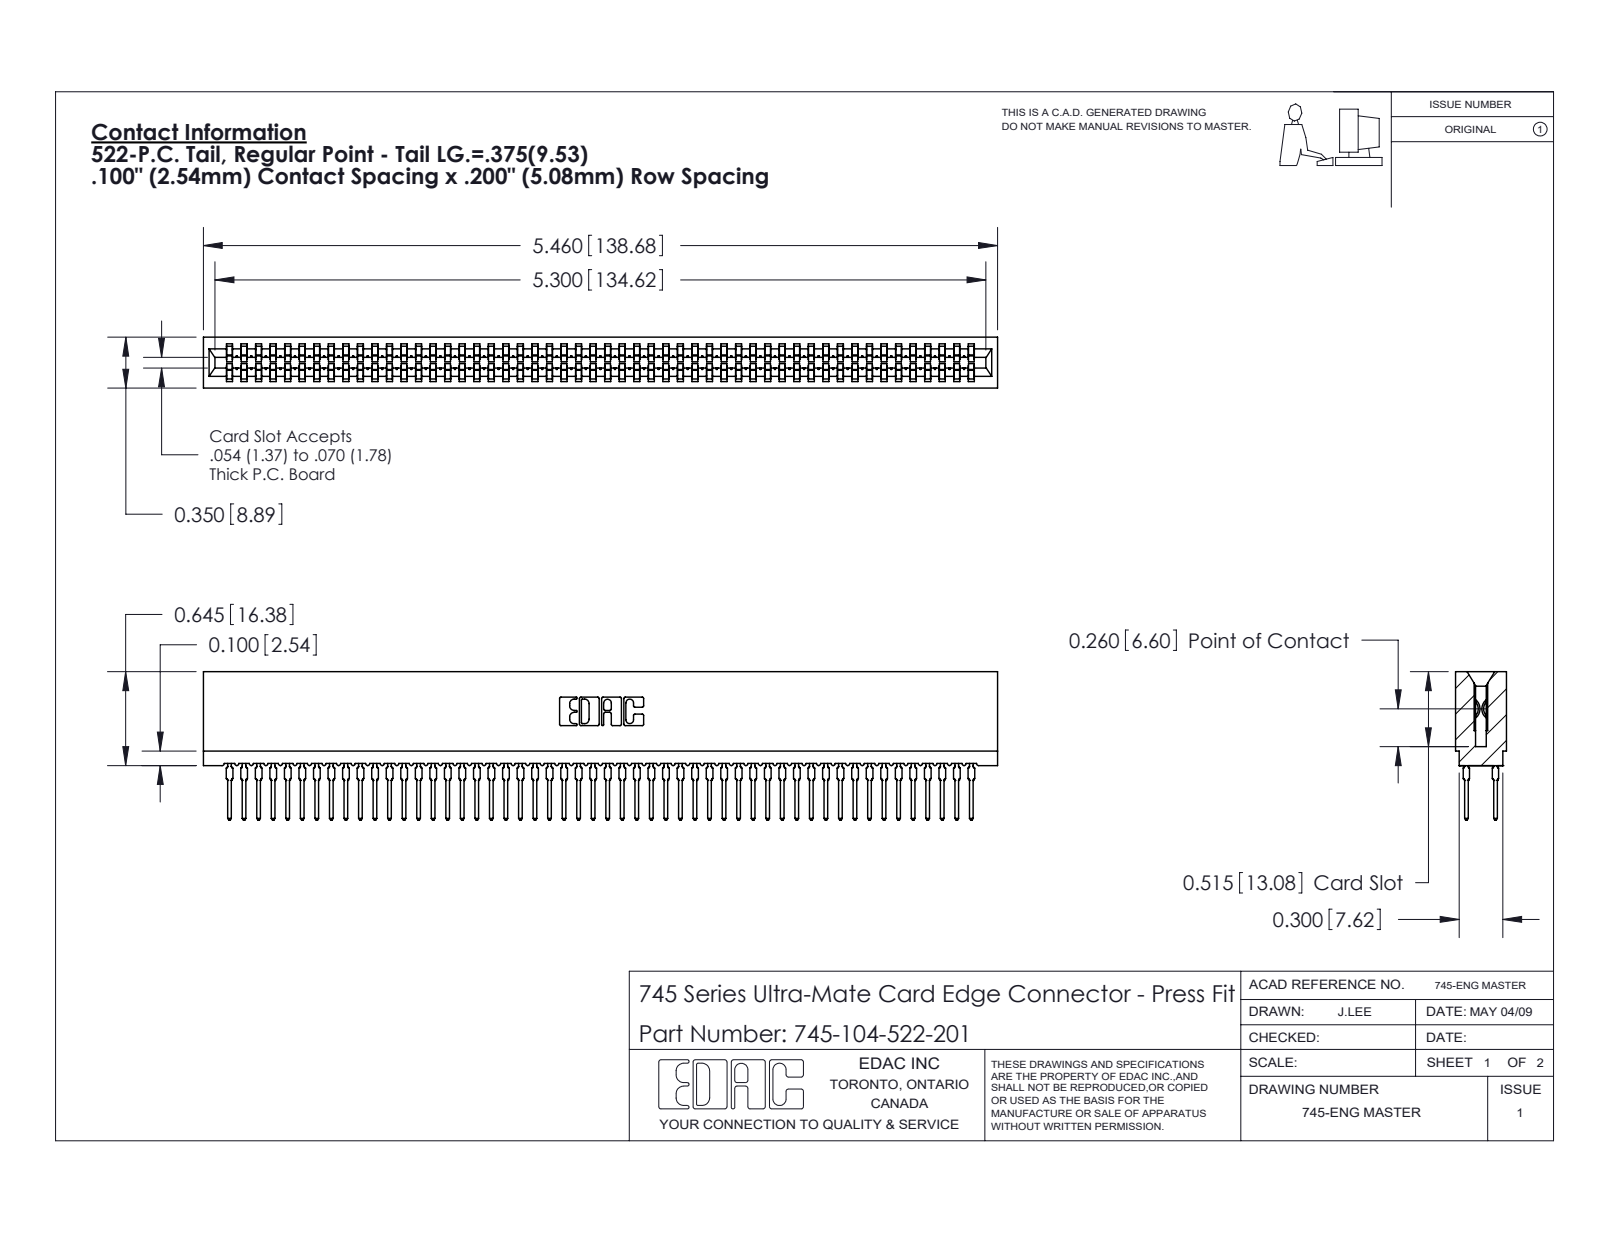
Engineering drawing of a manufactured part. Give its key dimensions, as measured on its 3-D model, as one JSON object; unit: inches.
{"part_name": "745-292-001_522; 745-104-522-201; 745 Part_Insulator Option - 01", "step_written_by": "SolidWorks 2020 (CONFIG_CONTROL_DESIGN)", "units": "inches", "bodies": {"solids": 105, "faces": 9403, "planar": 4839, "cylindrical": 1860, "other": 2704}, "overall_size": [5.46, 1.021, 0.35], "volume_in3": 0.765, "surface_area_in2": 40.43, "partial_cylinders_radius": [[0.021, 208], [0.015, 104], [0.01, 22], [0.005, 8], [0.011, 8], [0.007, 6], [0.031, 6], [0.026, 3]], "face_to_face_distances": [0.35, 0.063, 0.287, 0.2, 0.045, 0.305, 0.018, 0.243, 0.138, 0.212]}
